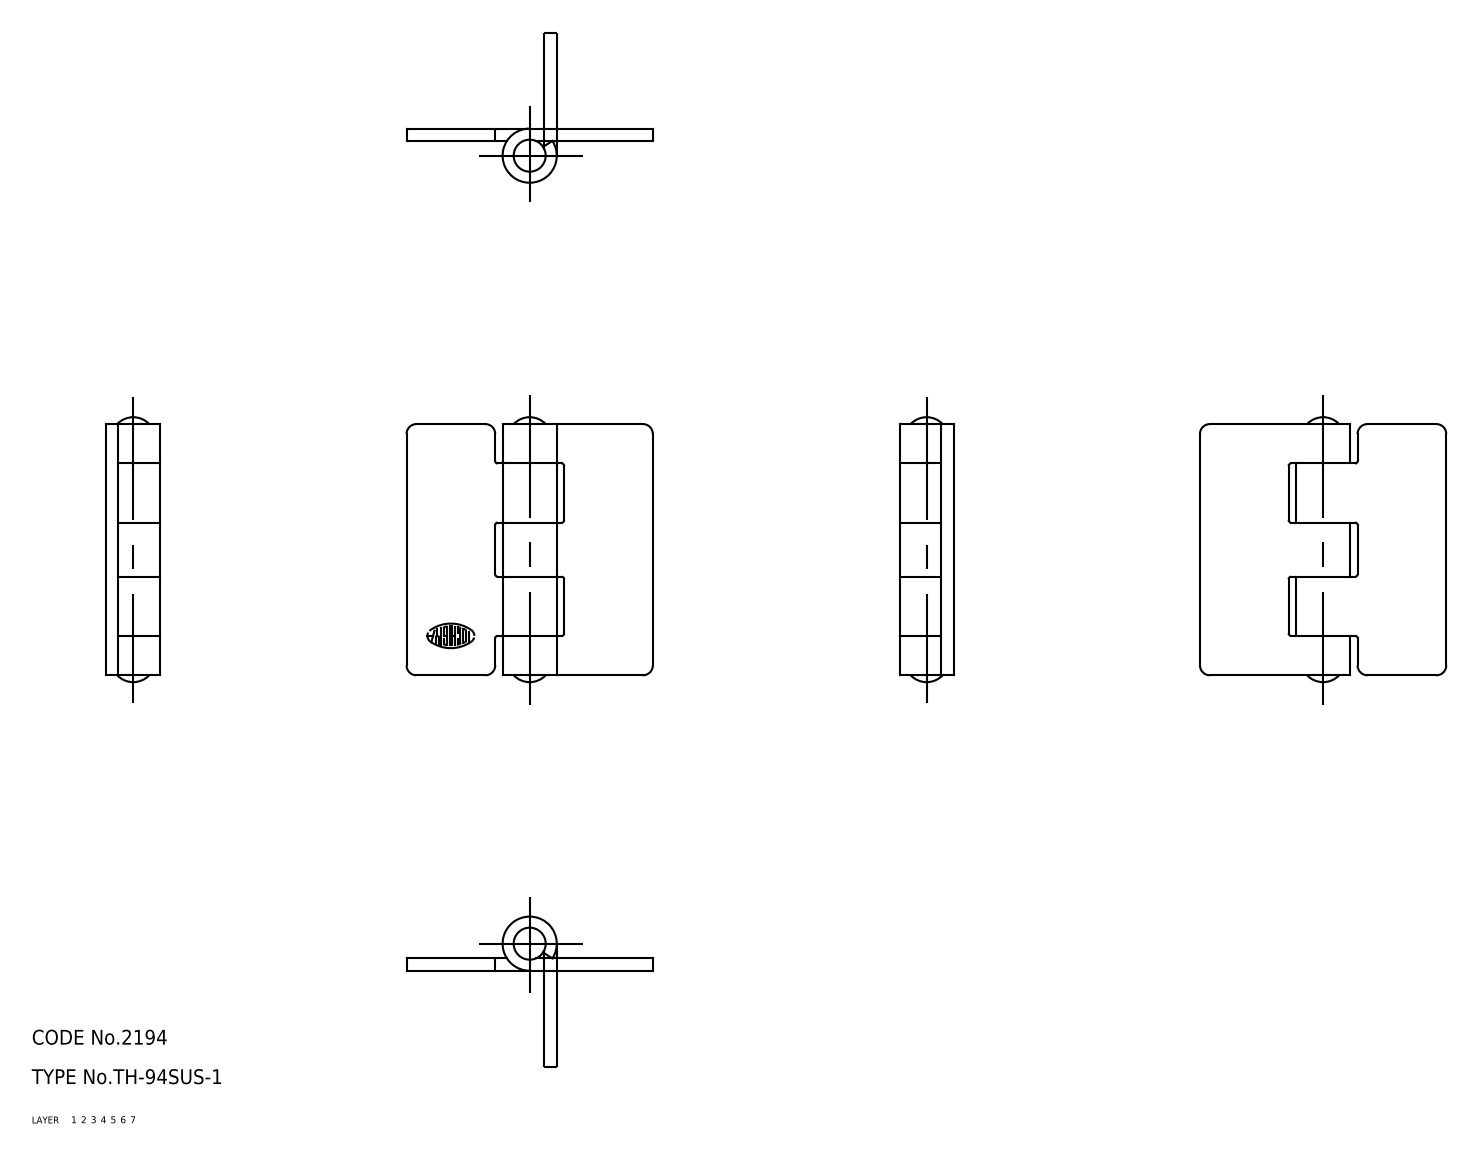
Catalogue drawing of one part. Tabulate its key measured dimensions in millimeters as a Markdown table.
| quantity | value |
| --- | --- |
| part name | hinge piece_B; hinge piece_A; shaft; TH_94SUS_1_19228_36 |
| STEP written by | CADfix (AUTOMOTIVE_DESIGN) |
| units | millimeters |
| bodies | 3 solids, 58 faces (0 planar, 0 cylindrical, 58 other) |
| overall size | 53.79 × 50 × 11 |
| volume | 9 825 mm³ |
| surface area | 9 124 mm² |
